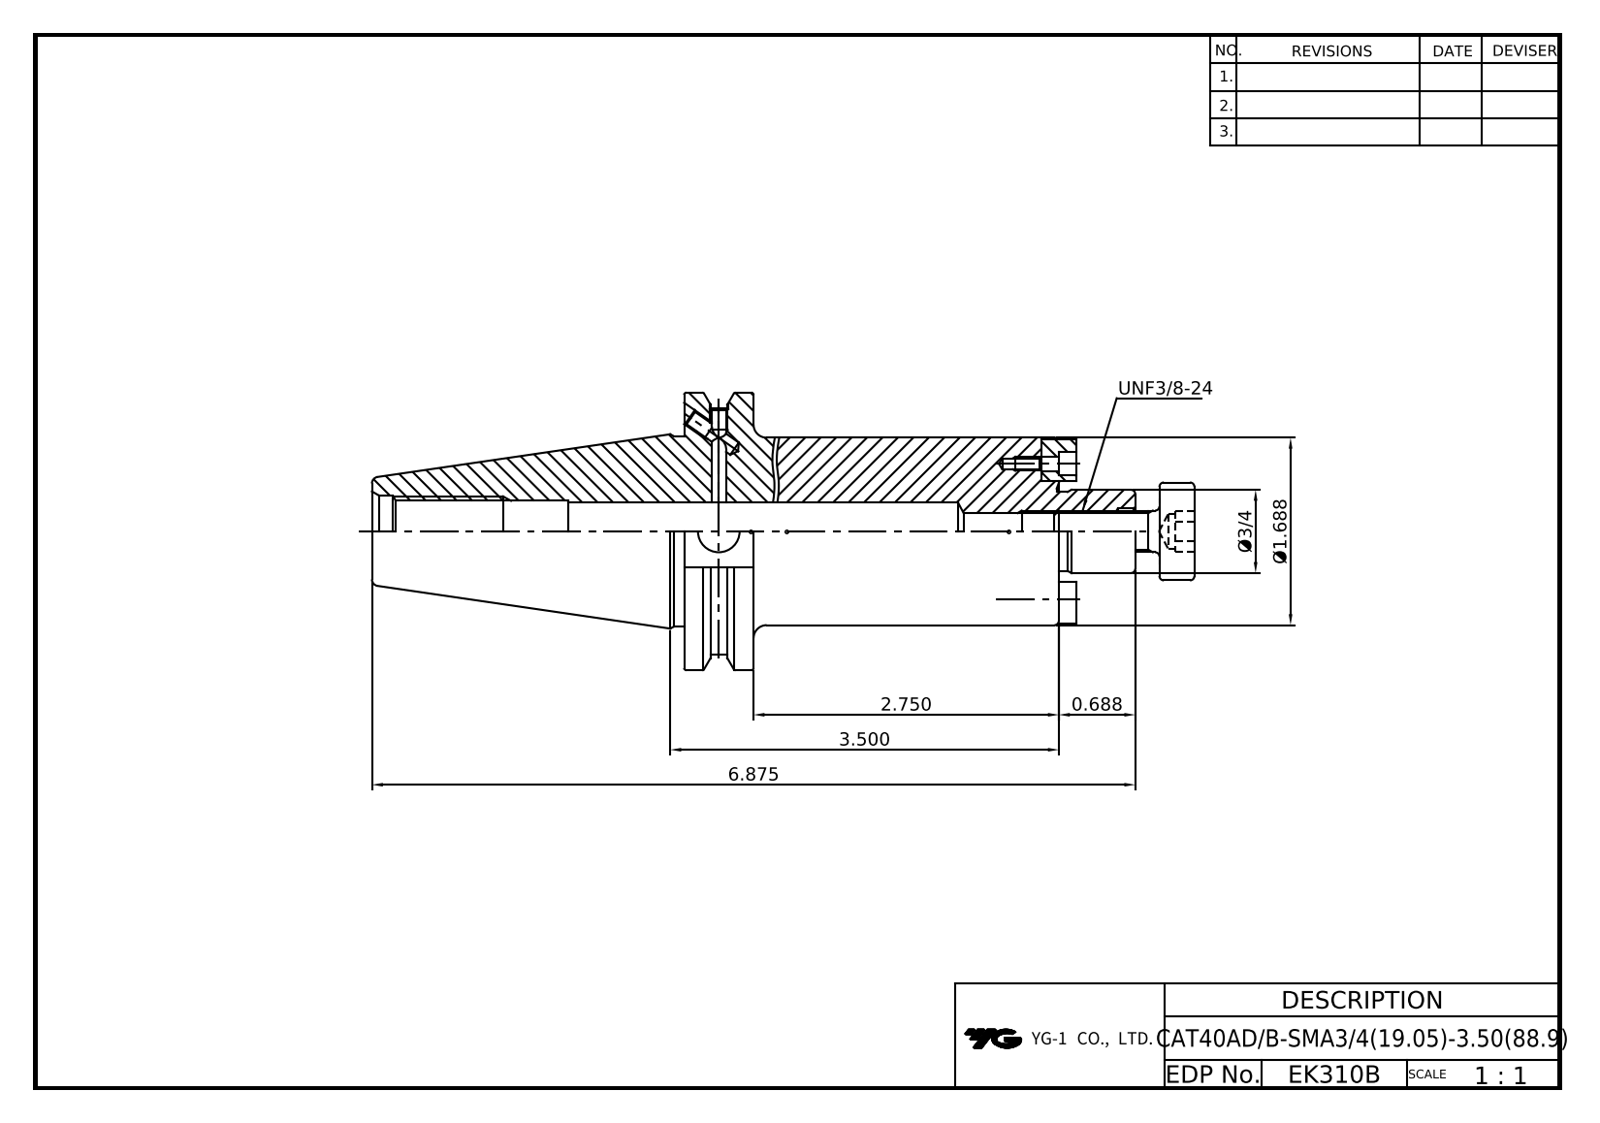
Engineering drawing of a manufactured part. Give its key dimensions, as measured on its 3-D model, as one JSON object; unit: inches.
{"part_name": "EK310B-CAT40ADB-SMA0_75-3_5; SMA19_05_DRIVE_KEY; SMA19_05_COLLAR_BOLT; EK310B-CAT40ADB-SMA0_75-3_5_ASM", "step_written_by": "PRO/ENGINEER BY PARAMETRIC TECHNOLOGY CORPORATION, 2012130 (CONFIG_CONTROL_DESIGN)", "units": "inches", "bodies": {"solids": 4, "faces": 245, "planar": 85, "cylindrical": 90, "other": 70}, "overall_size": [7.407, 2.5, 2.395], "volume_in3": 12.32, "surface_area_in2": 63.39, "round_holes": [[0.13, 5], [0.157, 3], [0.101, 2], [0.125, 2], [0.213, 2], [0.375, 2], [0.165, 1], [0.313, 1], [0.332, 1], [0.413, 1], [0.531, 1], [0.625, 1]], "round_bosses_or_shafts": [[2.5, 1], [1.717, 1], [1.688, 1], [0.882, 1], [0.75, 1], [0.726, 1], [0.375, 1], [0.332, 1]], "partial_cylinders_radius": [[0.155, 2], [0.156, 2], [1.108, 1]], "face_to_face_distances": [0.626, 3.375, 2.749, 4.595, 3.969, 1.22, 3.219, 2.593, 0.156, 1.376], "hole_center_spacings": [0.609, 1.218]}
